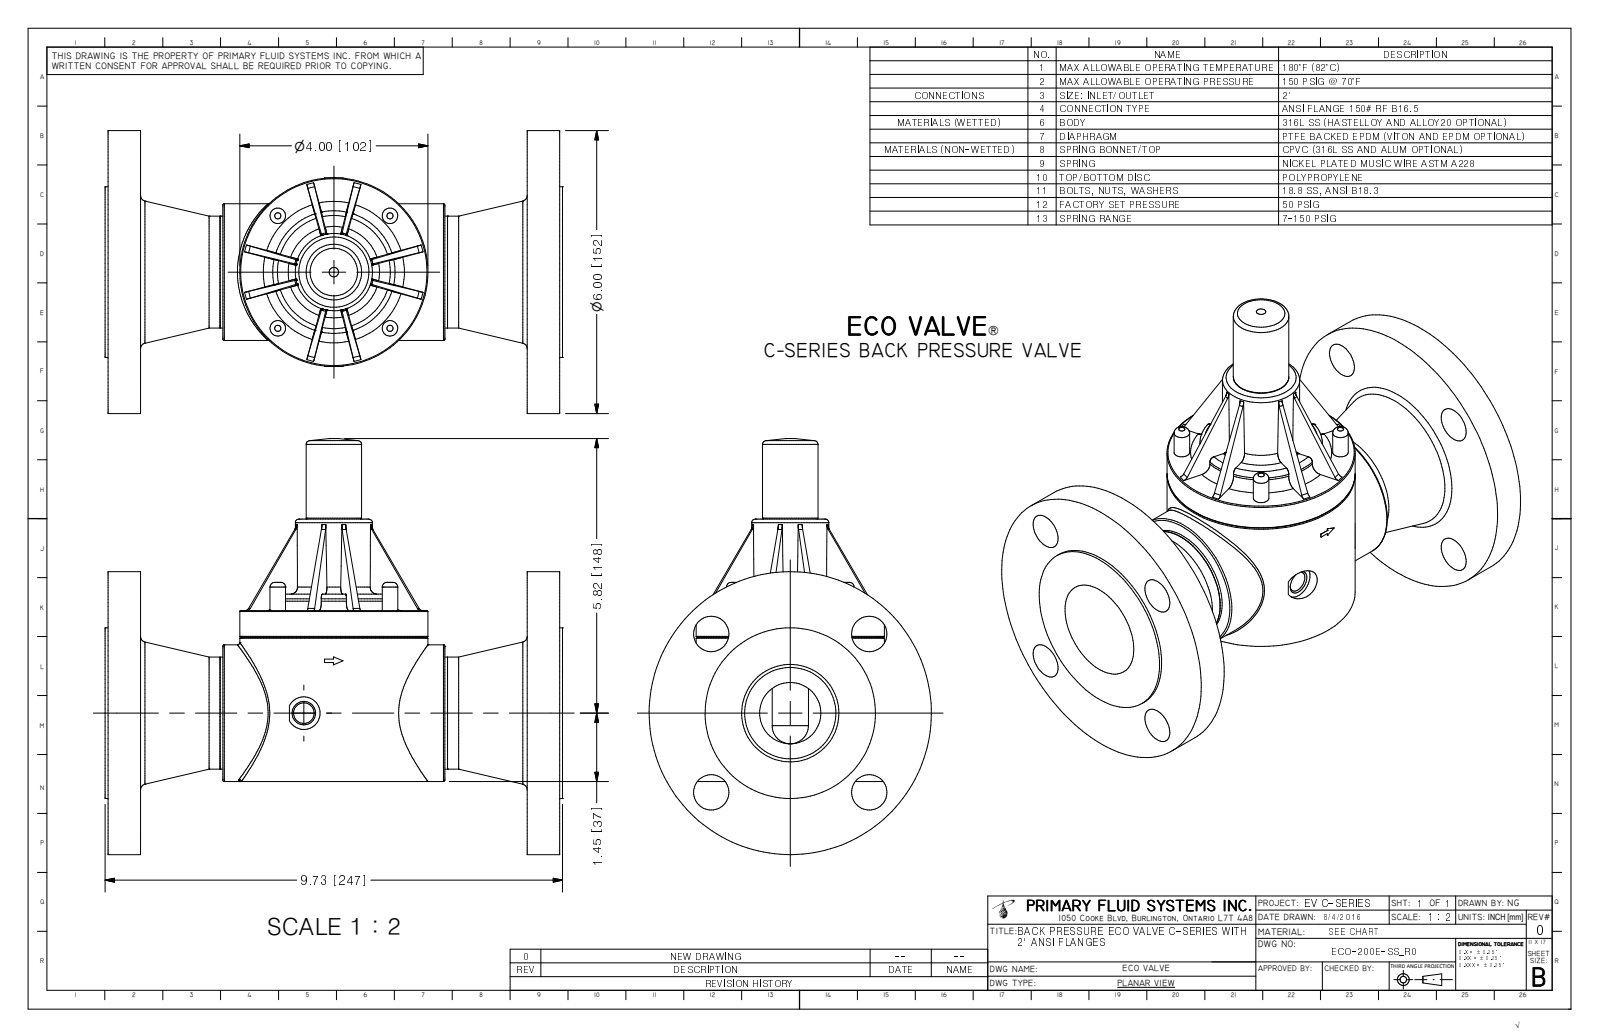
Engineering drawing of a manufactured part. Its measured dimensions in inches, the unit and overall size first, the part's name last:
Units: inches
Overall size (bounding box): 9.725 × 8.824 × 6
Round holes (diameter × count): ⌀0.23 ×4, ⌀0.4 ×4, ⌀0.75 ×4, ⌀0.257 ×1, ⌀0.438 ×1, ⌀0.691 ×1, ⌀2.067 ×1
Round bosses / shafts (diameter × count): ⌀0.33 ×4, ⌀0.256 ×4, ⌀6 ×1, ⌀4 ×1, ⌀3.62 ×1, ⌀2.9 ×1, ⌀2.6 ×1, ⌀2.375 ×1
Partial cylindrical surfaces — rounded edges, fillets, slot ends (radius × count): R0.1 ×8, R0.128 ×4, R0.129 ×3, R0.2 ×3
Main face-to-face distances: 0.69, 8.91, 8.22, 9.6, 0.063, 0.753, 8.972, 9.663, 2.503, 7.222
Hole centre spacings: 2.375, 2.385, 2.385, 2.386, 2.386, 3.359, 3.373, 3.374
Volume: 100.6 in³ · Surface area: 316.1 in²
Bodies: 1 solid, 248 faces (116 planar, 70 cylindrical, 62 other)
Part name (STEP PRODUCT): ECO-200E-SS_R0
STEP written by: Autodesk Inventor 2009 (AUTOMOTIVE_DESIGN)
